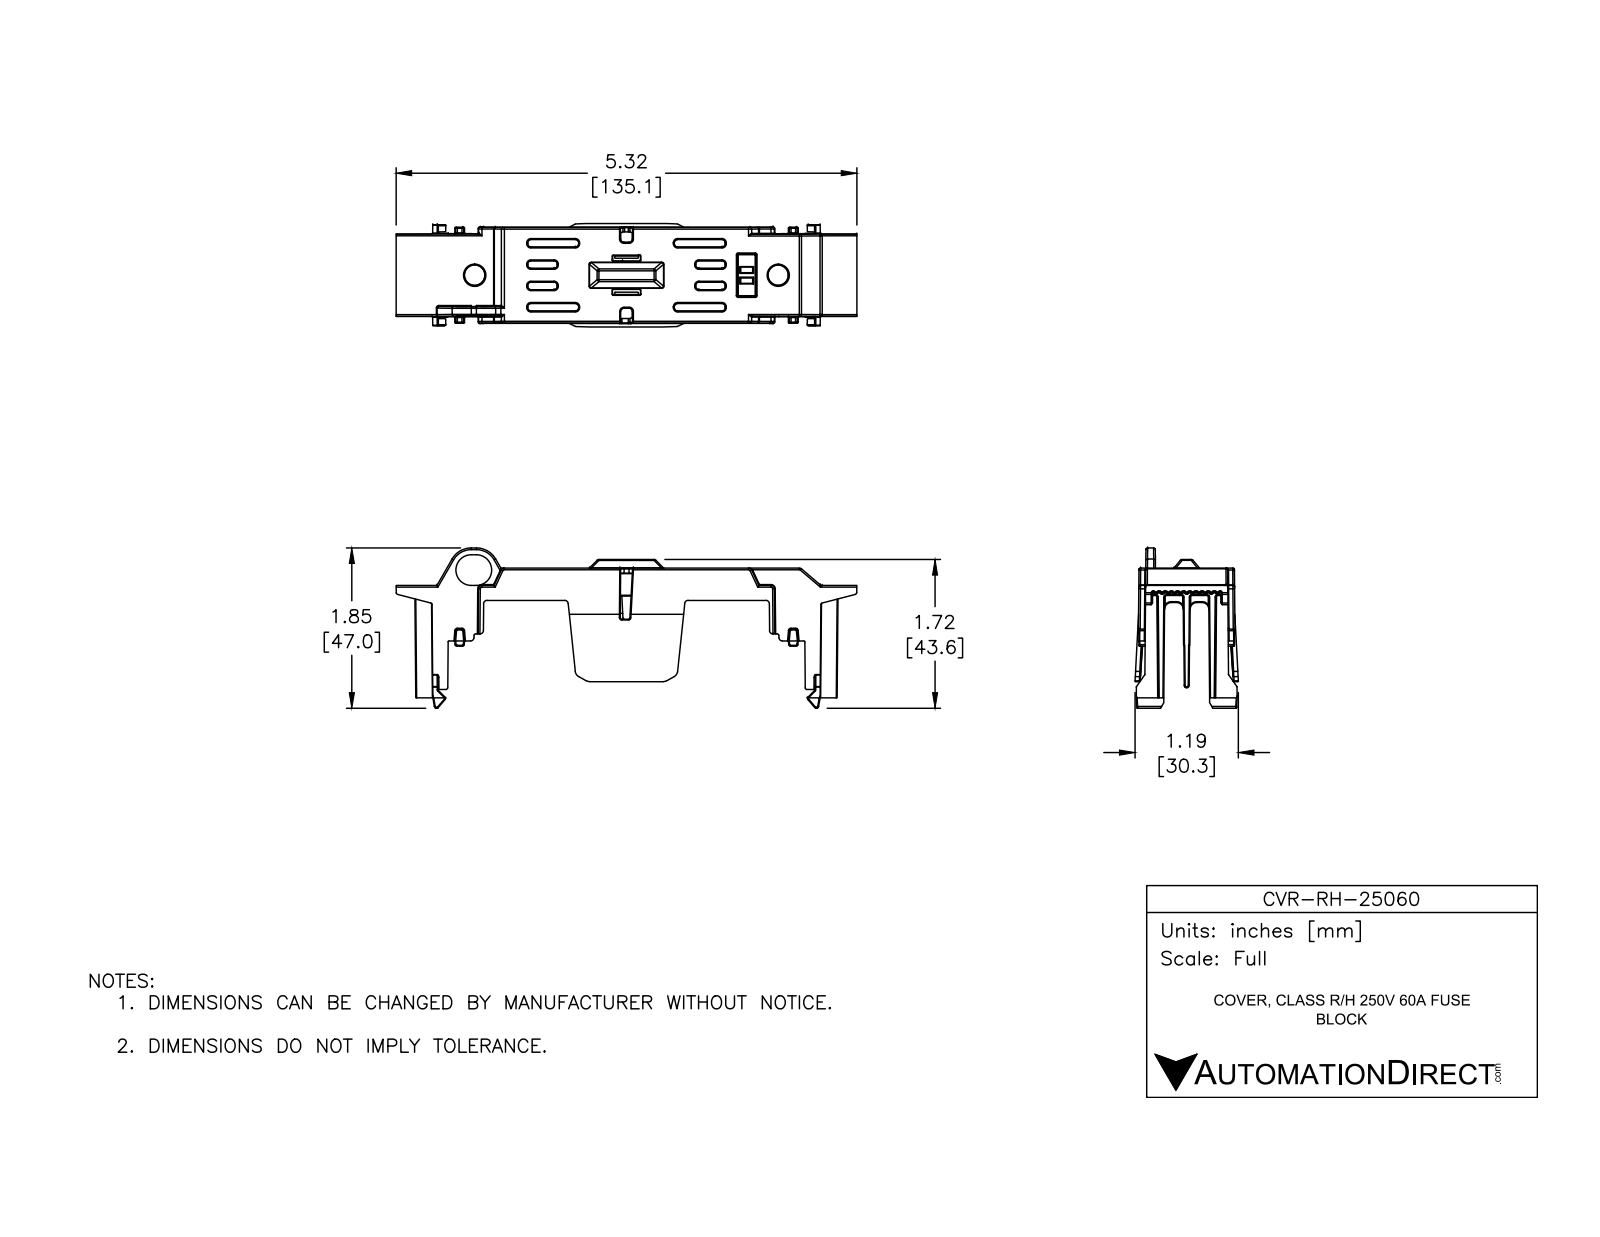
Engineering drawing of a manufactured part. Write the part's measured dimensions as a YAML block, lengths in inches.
part_name: "CVR-RH-25060"
step_written_by: "SolidWorks 2016 (AUTOMOTIVE_DESIGN)"
units: inches
bodies: {solids: 1, faces: 2347, planar: 462, cylindrical: 1041, other: 844}
overall_size: [5.318, 1.85, 1.193]
volume: 0.991
surface_area: 33.91
partial_cylinders:
  - {radius: 0.01, count: 346}
  - {radius: 0.006, count: 206}
  - {radius: 0.02, count: 70}
  - {radius: 0.039, count: 70}
  - {radius: 0.03, count: 10}
  - {radius: 0.079, count: 8}
  - {radius: 0.026, count: 2}
  - {radius: 0.177, count: 2}
face_to_face_distances: [0.059, 0.079, 0.059, 0.019, 0.201, 0.138, 0.142, 0.161, 0.24, 0.221]
